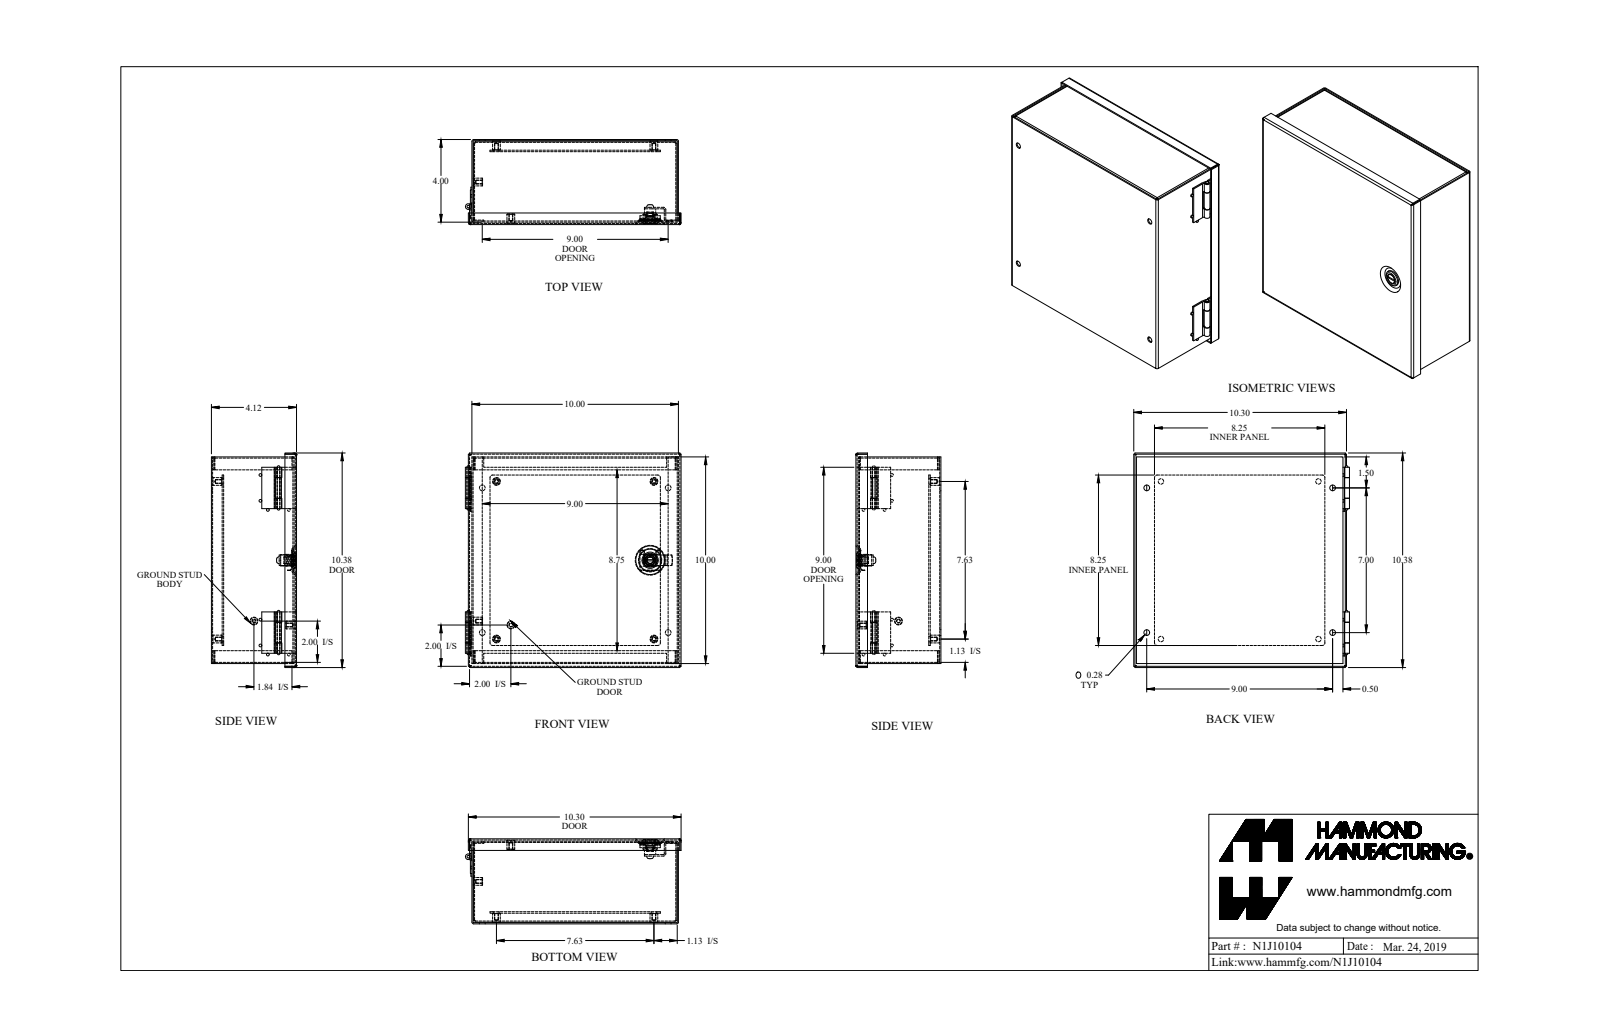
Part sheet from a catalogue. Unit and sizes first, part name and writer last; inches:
Units: inches
Overall size (bounding box): 10.443 × 10.38 × 4.118
Round holes (diameter × count): ⌀0.156 ×6, ⌀0.265 ×4, ⌀0.28 ×4, ⌀0.125 ×1, ⌀0.319 ×1, ⌀0.476 ×1
Round bosses / shafts (diameter × count): ⌀0.131 ×8, ⌀0.375 ×6, ⌀0.787 ×1, ⌀0.547 ×1, ⌀0.472 ×1, ⌀0.469 ×1, ⌀0.366 ×1, ⌀0.32 ×1
Partial cylindrical surfaces — rounded edges, fillets, slot ends (radius × count): R0.029 ×16, R0.086 ×16, R0.012 ×4, R0.1 ×4, R0.125 ×4, R0.036 ×2, R0.079 ×2, R0.25 ×2
Main face-to-face distances: 0.057, 4.061, 9.943, 4.004, 4.118, 10, 9.886, 0.072, 0.517, 0.46
Hole centre spacings: 0.755, 7.345, 7.625, 8.319, 11.071, 3.607, 3.817, 7
Volume: 29.81 in³ · Surface area: 1 013 in²
Bodies: 18 solids, 477 faces (224 planar, 188 cylindrical, 65 other)
Part name (STEP PRODUCT): N1J10104
STEP written by: SolidWorks 2018 (AUTOMOTIVE_DESIGN)
